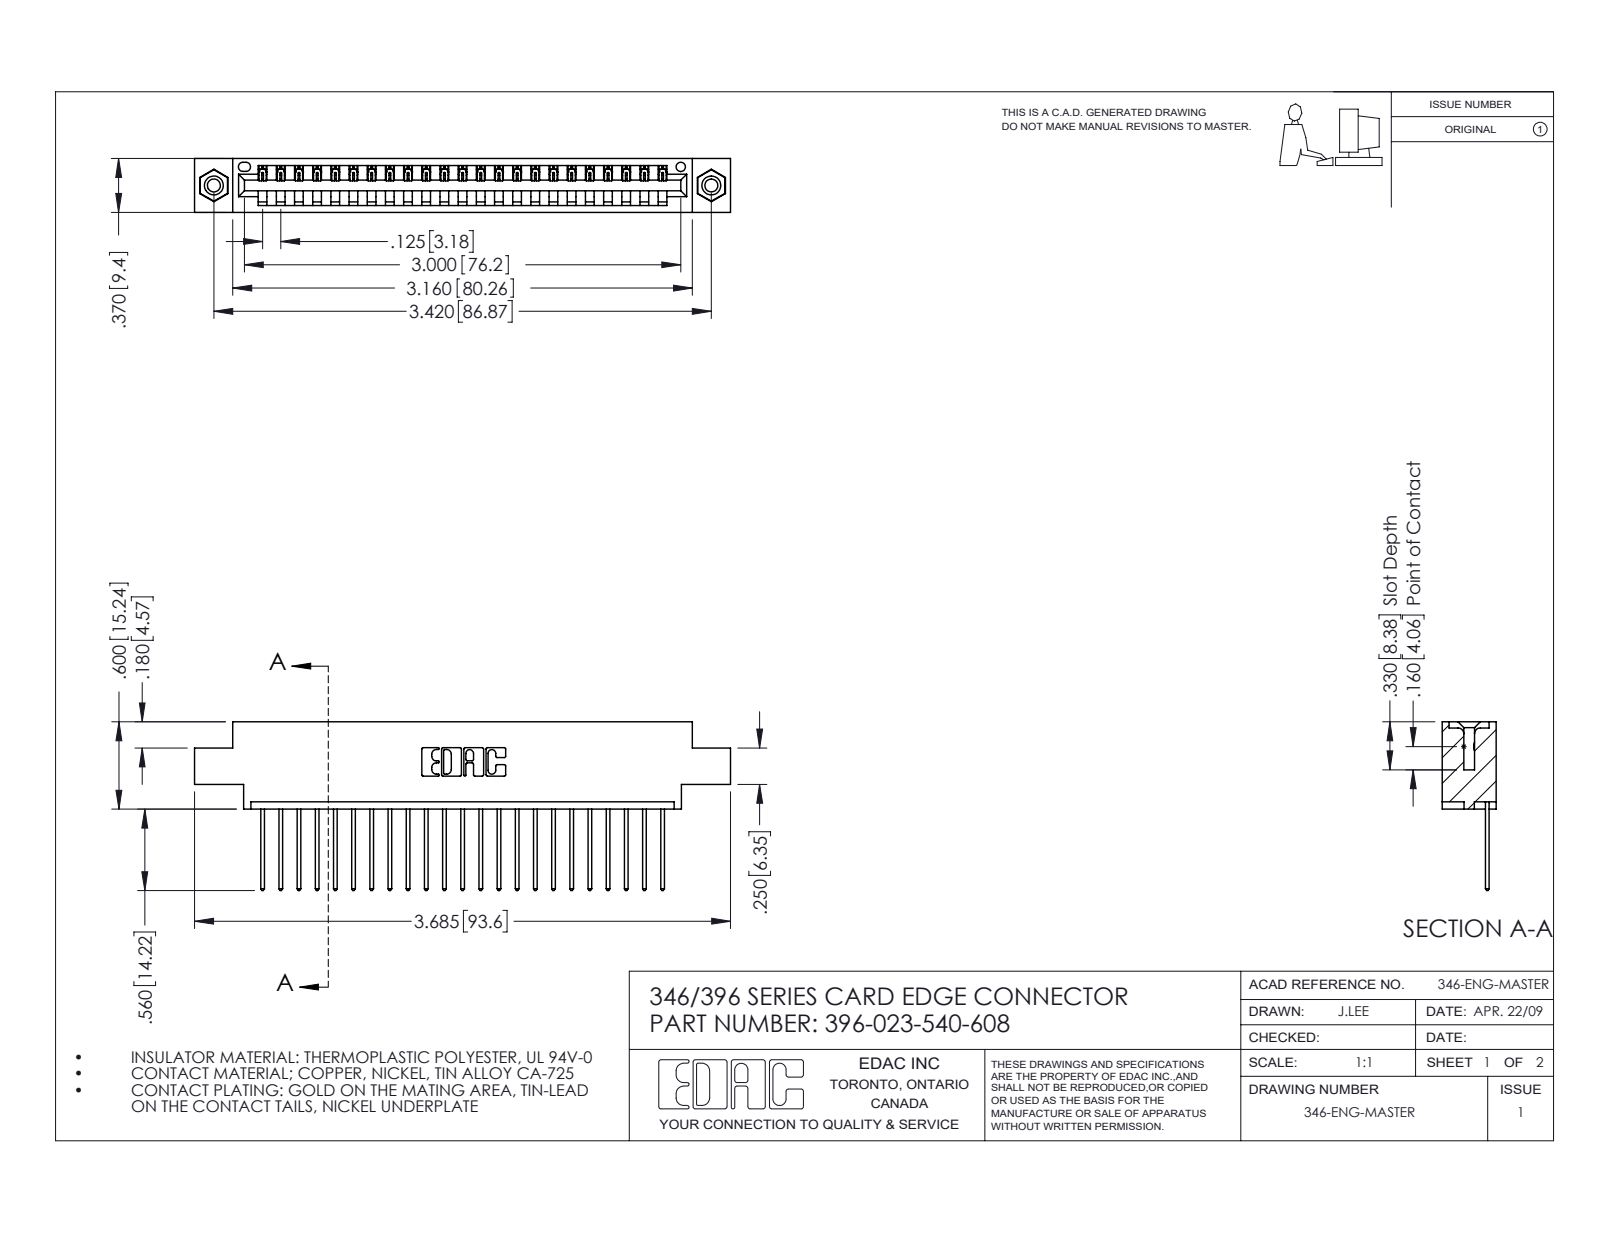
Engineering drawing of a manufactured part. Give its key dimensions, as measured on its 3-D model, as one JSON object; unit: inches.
{"part_name": "345-292-001_345-293-140; 396-023-540-608; 345-250-001_345-250-003-102; 346 Part_0.170 Offset - 0.156 Dia-TI", "step_written_by": "SolidWorks 2016 (CONFIG_CONTROL_DESIGN)", "units": "inches", "bodies": {"solids": 26, "faces": 1520, "planar": 1032, "cylindrical": 472, "other": 16}, "overall_size": [3.685, 1.16, 0.37], "volume_in3": 0.531, "surface_area_in2": 17.17, "round_holes": [[0.089, 2], [0.125, 2], [0.156, 2], [0.064, 1]], "round_bosses_or_shafts": [[0.155, 2]], "partial_cylinders_radius": [[0.006, 46], [0.01, 46], [0.01, 22], [0.007, 6], [0.031, 6], [0.026, 3], [0.031, 2], [0.04, 2]], "face_to_face_distances": [0.048, 0.322, 0.37, 0.25, 0.072, 0.298, 0.025, 0.222, 0.148, 0.1], "hole_center_spacings": [0.246, 3.212, 3.42]}
